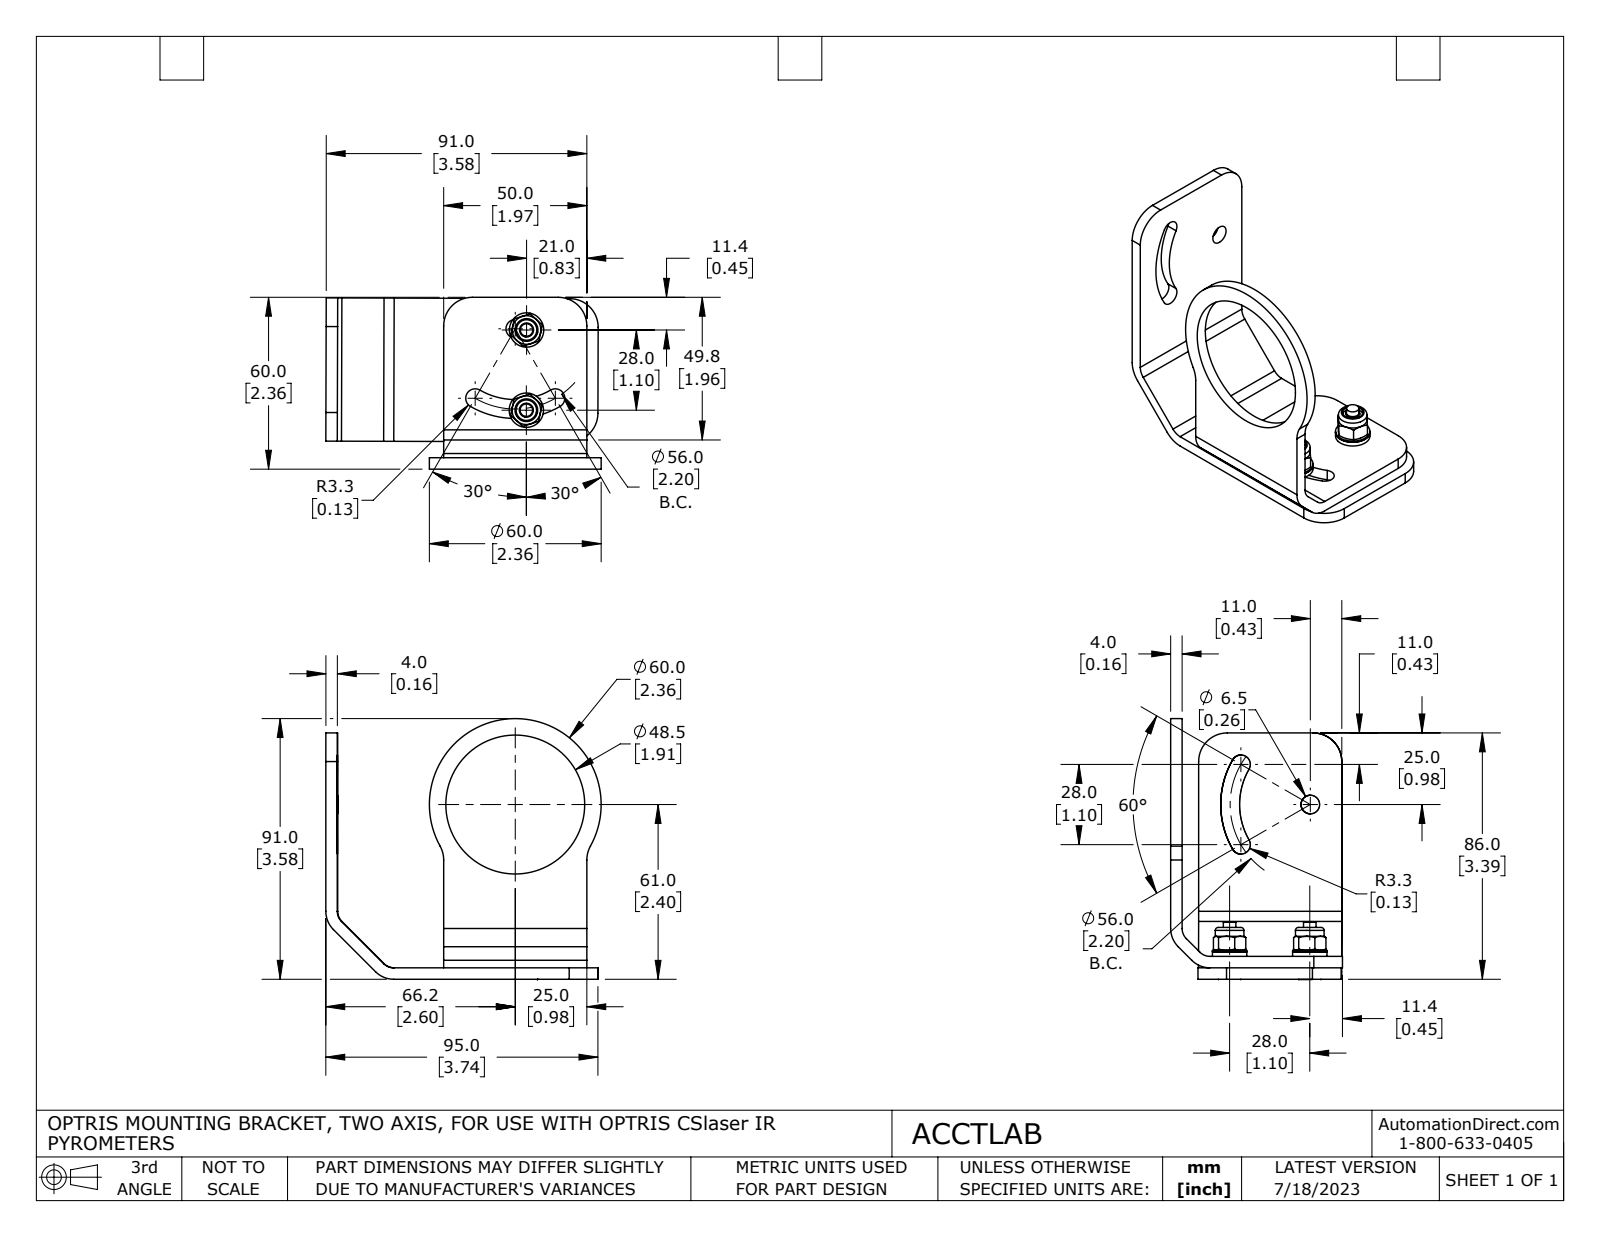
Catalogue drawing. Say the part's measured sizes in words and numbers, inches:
The part is named "ACCTLAB - Mounting bracket CxL CxV, adjustable in two axes NC coord fxt". Its 3-D file was written by "SolidWorks 2021 (AUTOMOTIVE_DESIGN)". It is 10 solids with 509 faces: 149 planar, 156 cylindrical and 204 other. Overall it measures 3.786 by 3.587 by 2.362 inches. Its volume is 3.215 cubic inches and its surface area 50.97 square inches. Round holes: 2 of diameter 0.197, 2 of diameter 0.252, 2 of diameter 0.256, 2 of diameter 0.281, 1 of diameter 1.909. Round bosses or shafts: 2 of diameter 0.472, 2 of diameter 0.394, 2 of diameter 0.299, 2 of diameter 0.236, 2 of diameter 0.172. Partial cylindrical surfaces (rounded edges, fillets, slot ends): 8 of radius 0.394, 4 of radius 0.13, 4 of radius 0.197, 4 of radius 0.354, 2 of radius 0.972, 2 of radius 1.232, 1 of radius 0.133, 1 of radius 0.133. The main face-to-face distances are 0.157, 0.315, 1.969, 0.378, 0.22, 0.063, 0.398, 0.02, 0.24, 0.083. The hole center spacings are 0.156, 1.102, 1.129.
